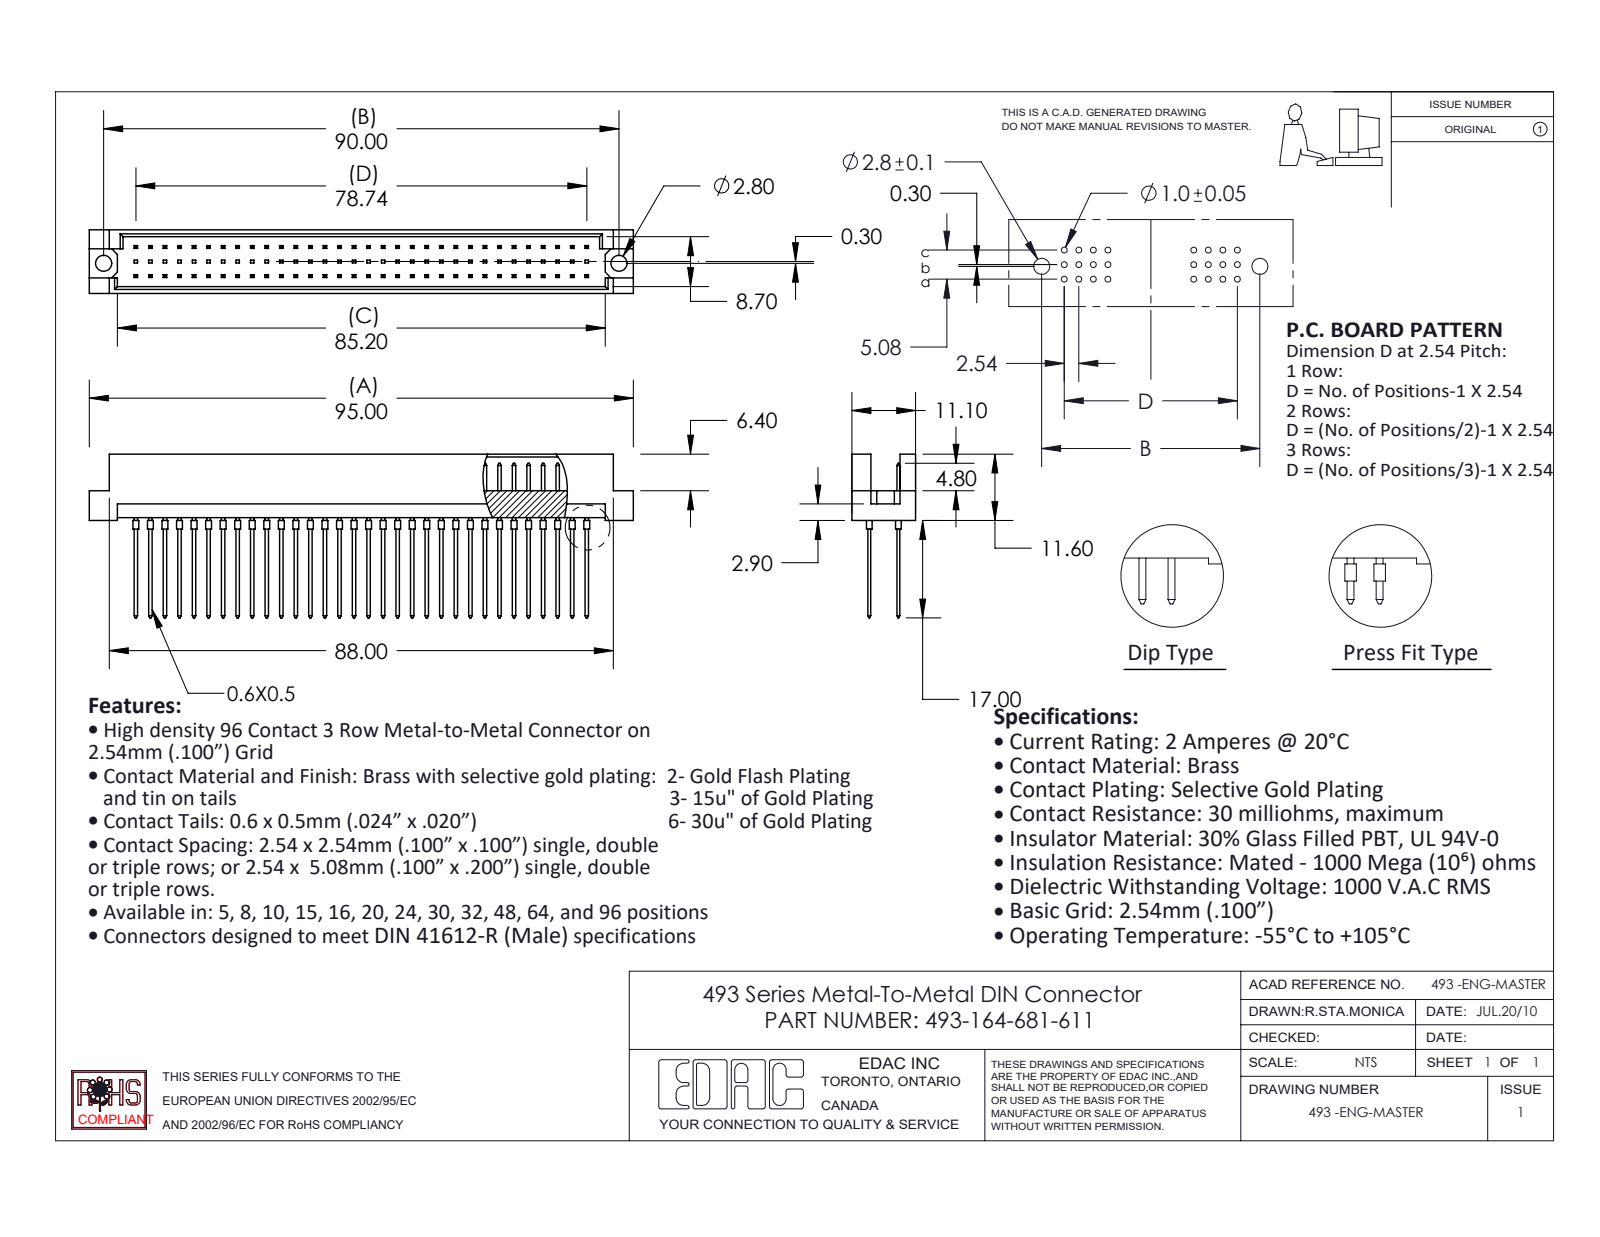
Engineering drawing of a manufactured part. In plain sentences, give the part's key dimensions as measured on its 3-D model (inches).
The part is named "493-164-681-611; 493-290_81; 493 Part_96". Its 3-D file was written by "SolidWorks 2020 (CONFIG_CONTROL_DESIGN)". It is 65 solids with 1844 faces: 1712 planar, 132 cylindrical and 0 other. Overall it measures 3.74 by 1.126 by 0.437 inches. Its volume is 0.379 cubic inches and its surface area 16.13 square inches. Round holes: 2 of diameter 0.11. Round bosses or shafts: 64 of diameter 0.039. The main face-to-face distances are 0.2, 0.047, 0.39, 0.02, 0.109, 0.128, 0.309, 0.328, 0.061, 0.081. The hole center spacings are 3.543.
